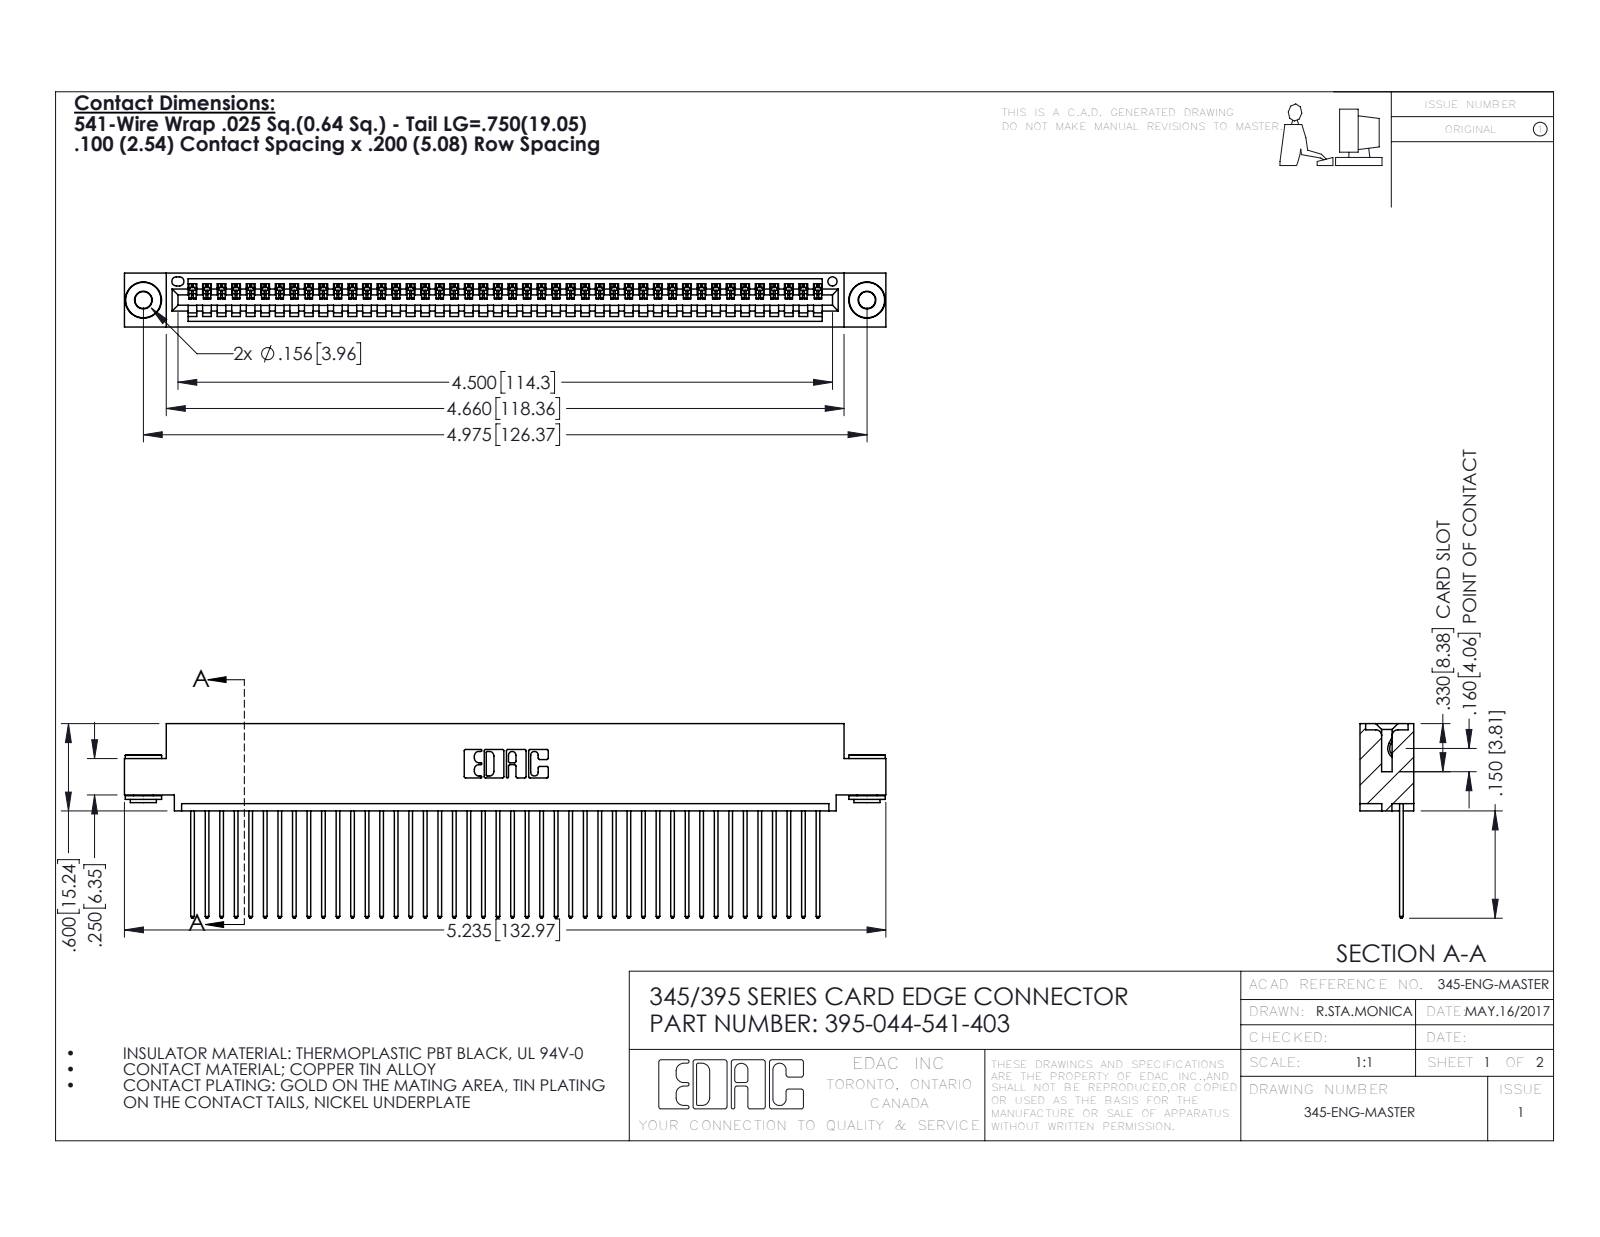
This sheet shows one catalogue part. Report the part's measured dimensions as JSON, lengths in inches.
{"part_name": "345-292-001_345-293-141; 345 Part_0.110 Offset - 0.156 Dia-TH; 345-250-002_345-250-002-102; 395-044-541-403", "step_written_by": "SolidWorks 2016 (CONFIG_CONTROL_DESIGN)", "units": "inches", "bodies": {"solids": 47, "faces": 2720, "planar": 1854, "cylindrical": 858, "other": 8}, "overall_size": [5.235, 1.337, 0.37], "volume_in3": 0.777, "surface_area_in2": 28.06, "round_holes": [[0.116, 2], [0.156, 2], [0.064, 1]], "round_bosses_or_shafts": [[0.25, 2], [0.18, 2], [0.136, 2]], "partial_cylinders_radius": [[0.006, 88], [0.01, 88], [0.01, 22], [0.007, 6], [0.031, 6], [0.026, 3], [0.031, 2], [0.04, 2]], "face_to_face_distances": [0.072, 0.298, 0.025, 0.098, 0.272, 0.37, 0.2, 0.225, 0.149, 0.072], "hole_center_spacings": [0.27, 4.739, 4.975]}
